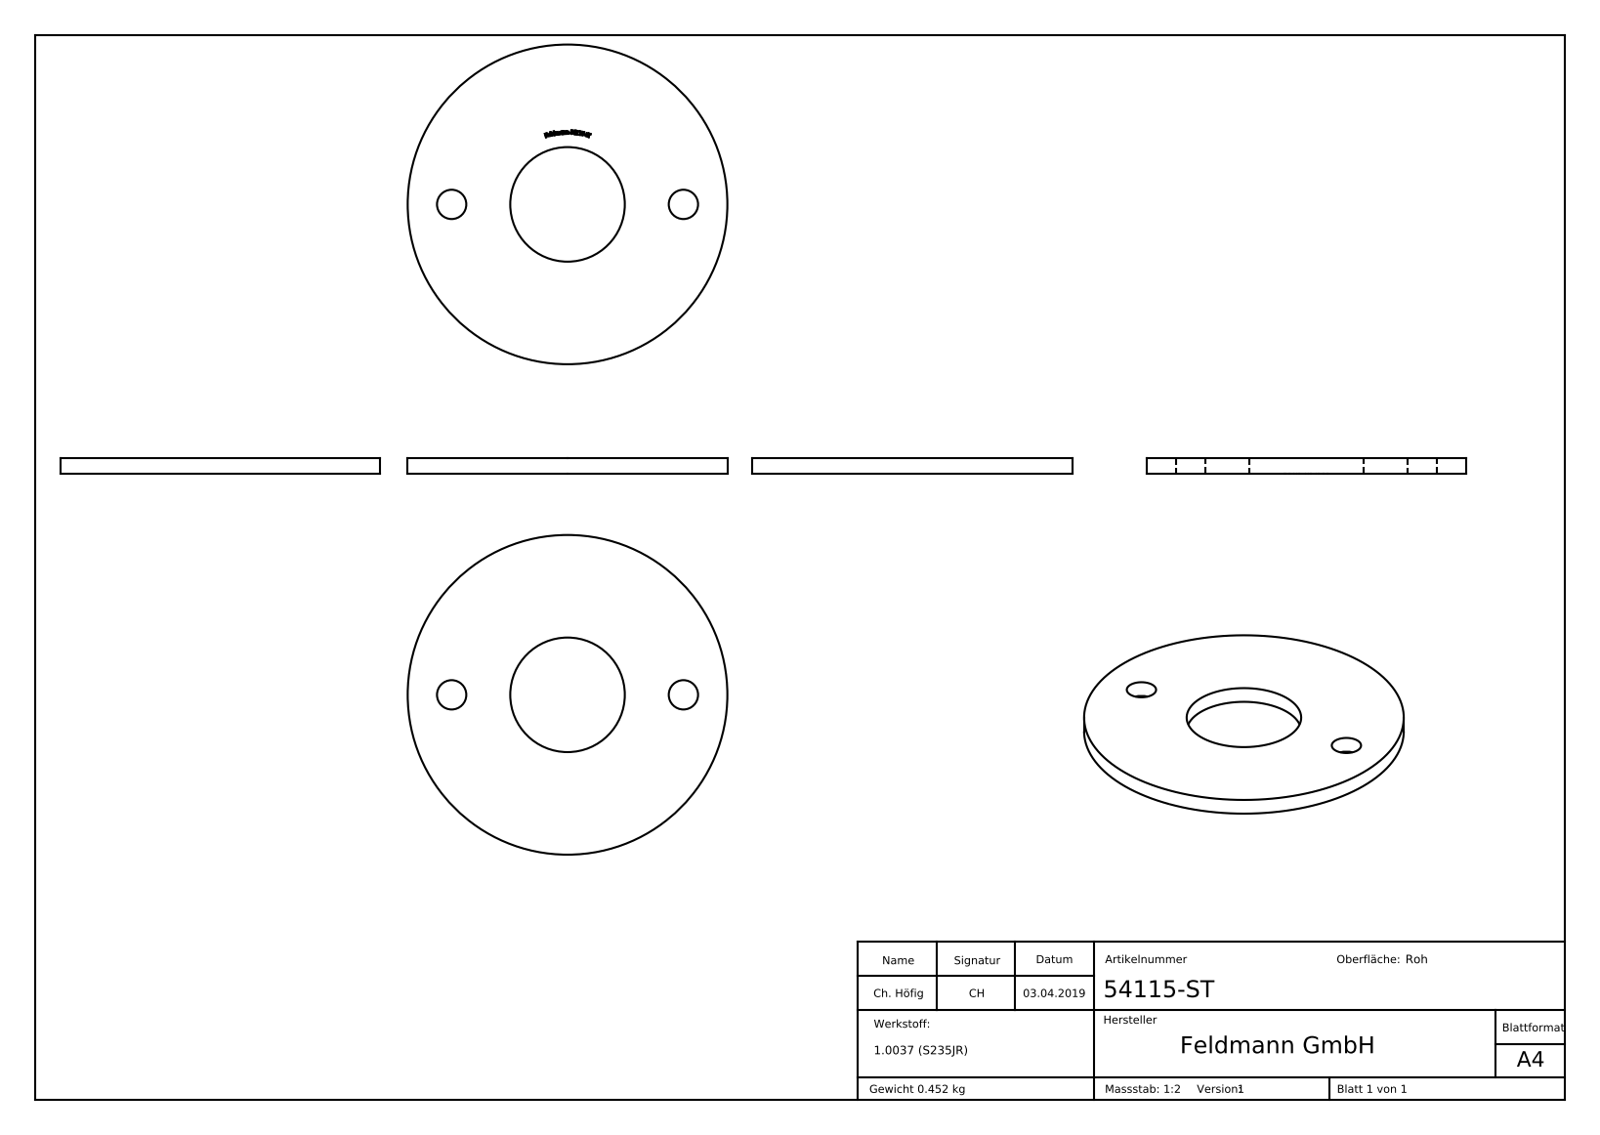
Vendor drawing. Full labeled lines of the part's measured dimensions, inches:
Part name (STEP PRODUCT): 54115-ST
STEP written by: SolidWorks 2015 (CONFIG_CONTROL_DESIGN)
Units: inches
Bodies: 1 solid, 214 faces (127 planar, 8 cylindrical, 79 other)
Overall size (bounding box): 4.724 × 4.724 × 0.236
Volume: 3.54 in³ · Surface area: 35.39 in²
Round holes (diameter × count): ⌀0.433 ×2, ⌀1.693 ×1
Round bosses / shafts (diameter × count): ⌀4.724 ×1
Main face-to-face distances: 0.236, 0.232, 0.028, 0.033, 0.021, 0.052, 0.057, 0.022, 0.017, 0.026
Hole centre spacings: 1.713, 3.425
